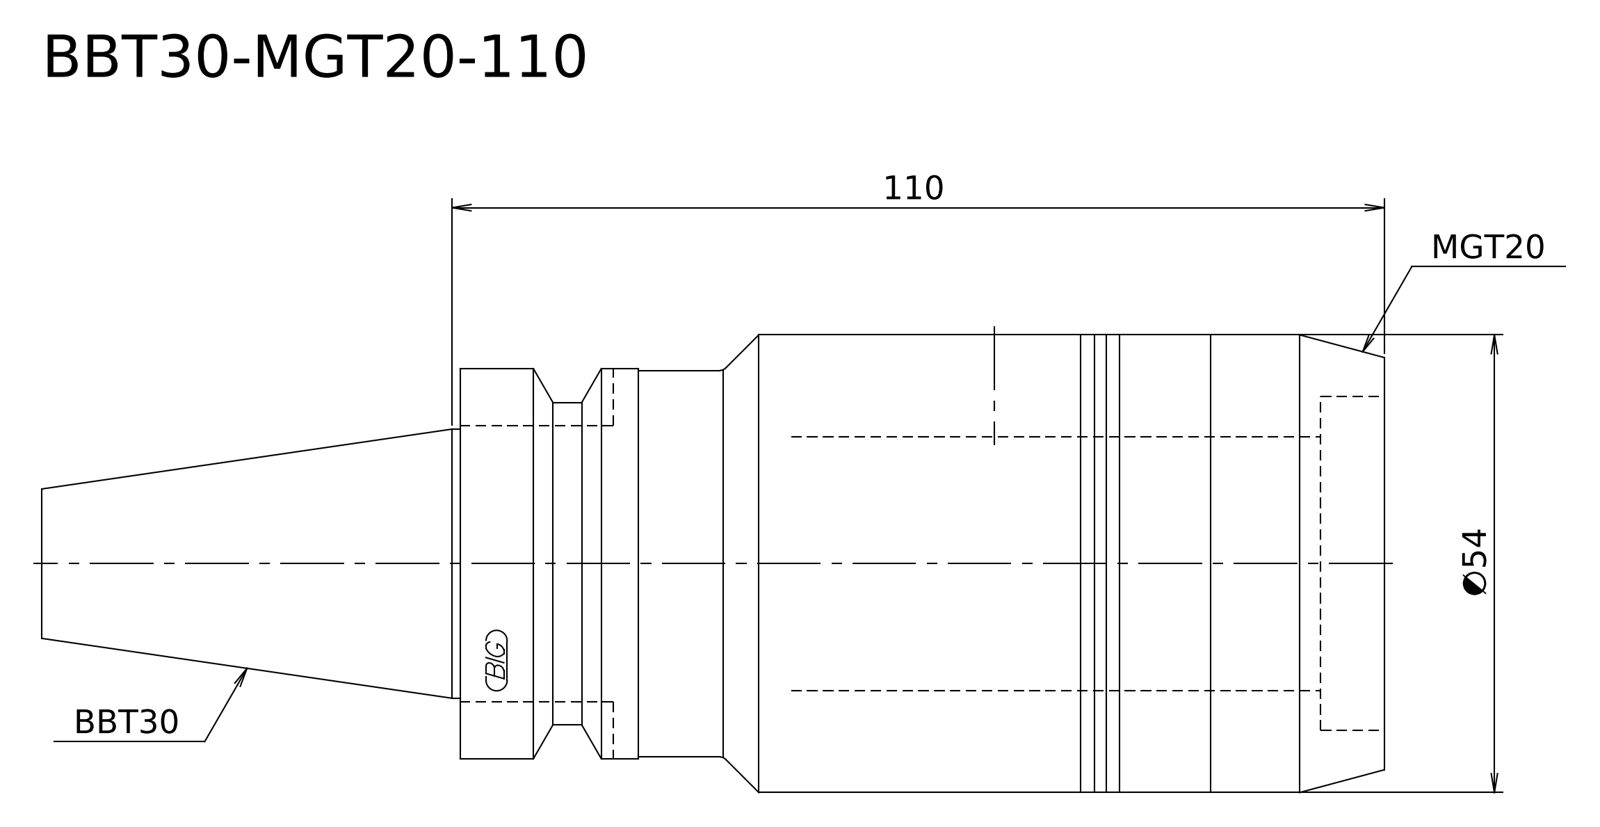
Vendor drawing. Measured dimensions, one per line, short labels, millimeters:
written by: Kubotek KeyCreator V8.5.1 (14335) (CONFIG_CONTROL_DESIGN)
unit: mm
bodies: 1 solid, 16 faces (4 planar, 6 cylindrical, 6 other)
size: 158.4 × 54 × 54
volume: 247 817 mm³; area: 25 242 mm²
bosses: 1× ⌀54, 1× ⌀46, 1× ⌀45.6, 1× ⌀38, 1× ⌀31.75
face distances: 109, 158.4, 49.4, 88, 21, 70.4
